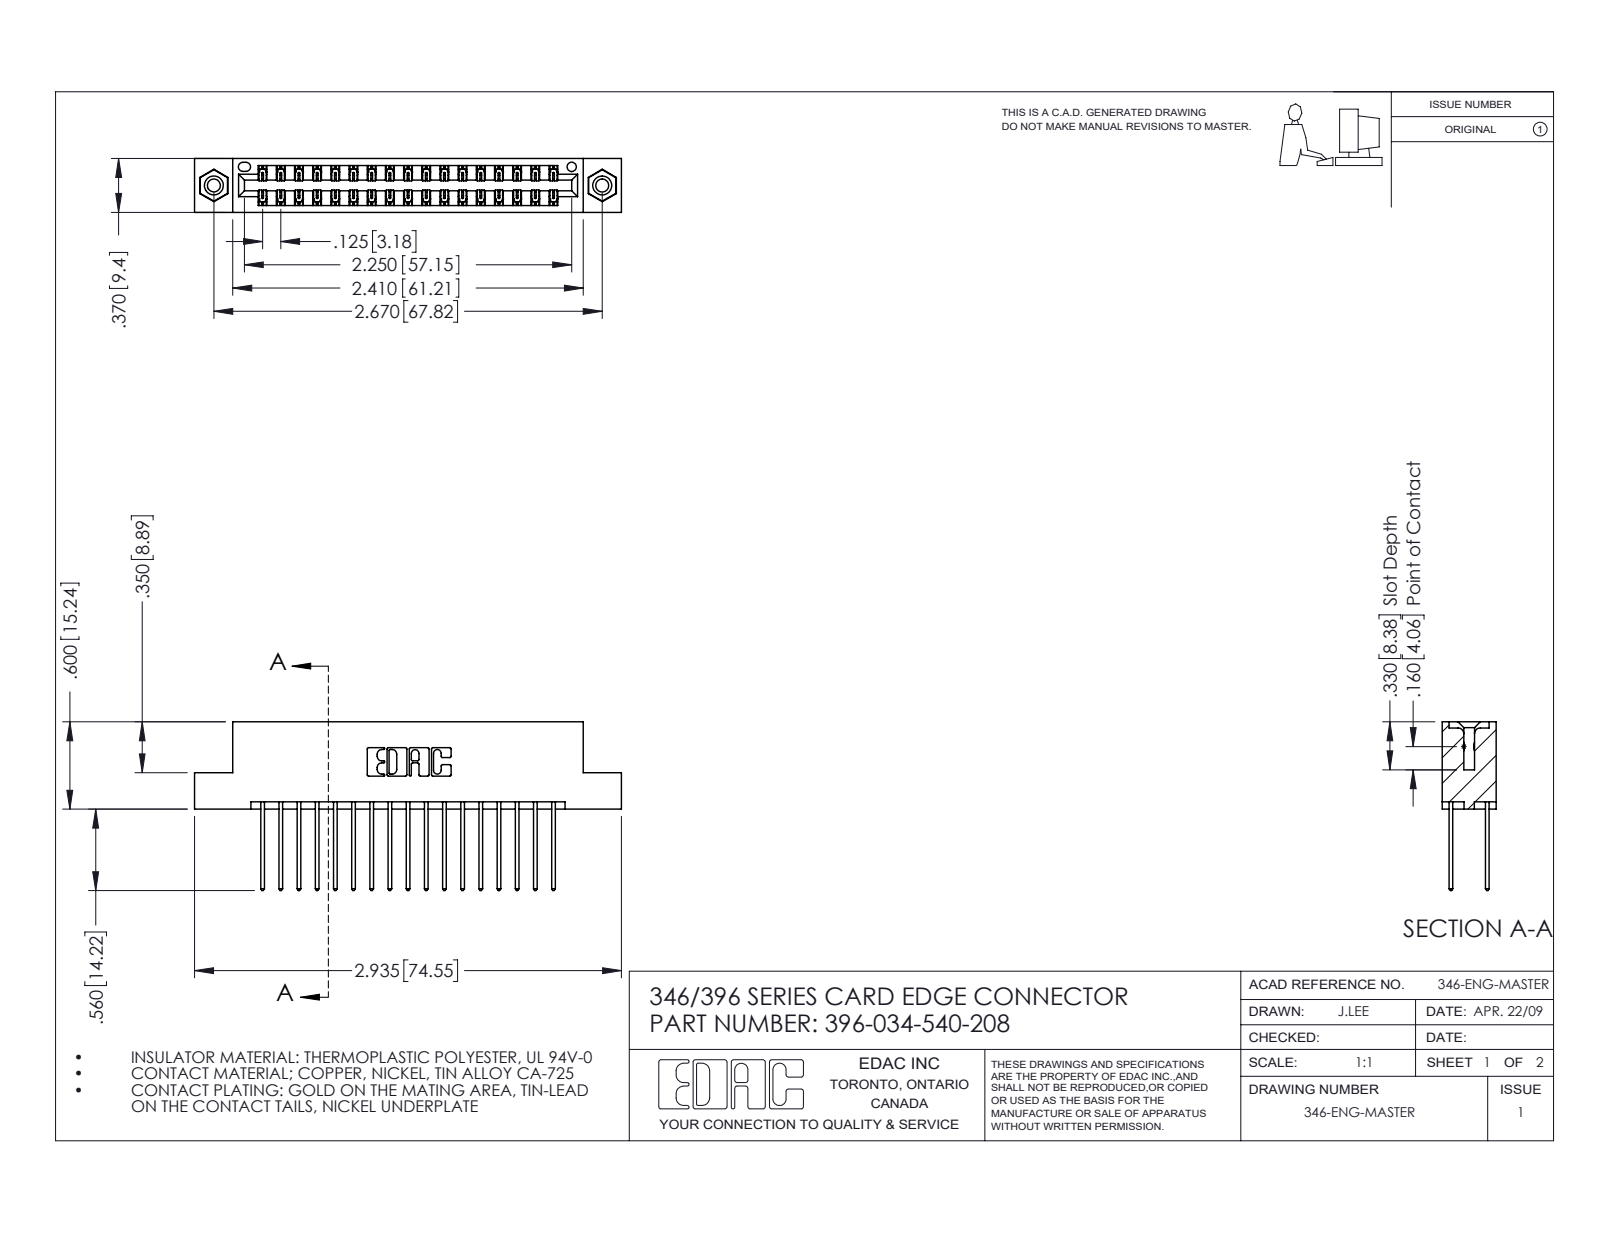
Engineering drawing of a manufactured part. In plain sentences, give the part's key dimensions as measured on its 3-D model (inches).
The part is named "345-250-001_345-250-003-102; 396-034-540-208; 345-292-001_345-293-140; 346 Part_Flush Mounting Lugs - 0.156 Dia-TI". Its 3-D file was written by "SolidWorks 2016 (CONFIG_CONTROL_DESIGN)". It is 37 solids with 1950 faces: 1298 planar, 636 cylindrical and 16 other. Overall it measures 2.935 by 1.16 by 0.37 inches. Its volume is 0.439 cubic inches and its surface area 15.7 square inches. Round holes: 2 of diameter 0.089, 2 of diameter 0.125, 2 of diameter 0.156, 1 of diameter 0.064. Round bosses or shafts: 2 of diameter 0.155. Partial cylindrical surfaces (rounded edges, fillets, slot ends): 51 of radius 0.006, 34 of radius 0.01, 22 of radius 0.01, 6 of radius 0.007, 6 of radius 0.031, 3 of radius 0.026, 2 of radius 0.014, 2 of radius 0.022. The main face-to-face distances are 0.048, 0.322, 0.25, 0.37, 0.072, 0.298, 0.025, 0.275, 0.148, 0.222. The hole center spacings are 0.246, 2.463, 2.67.
